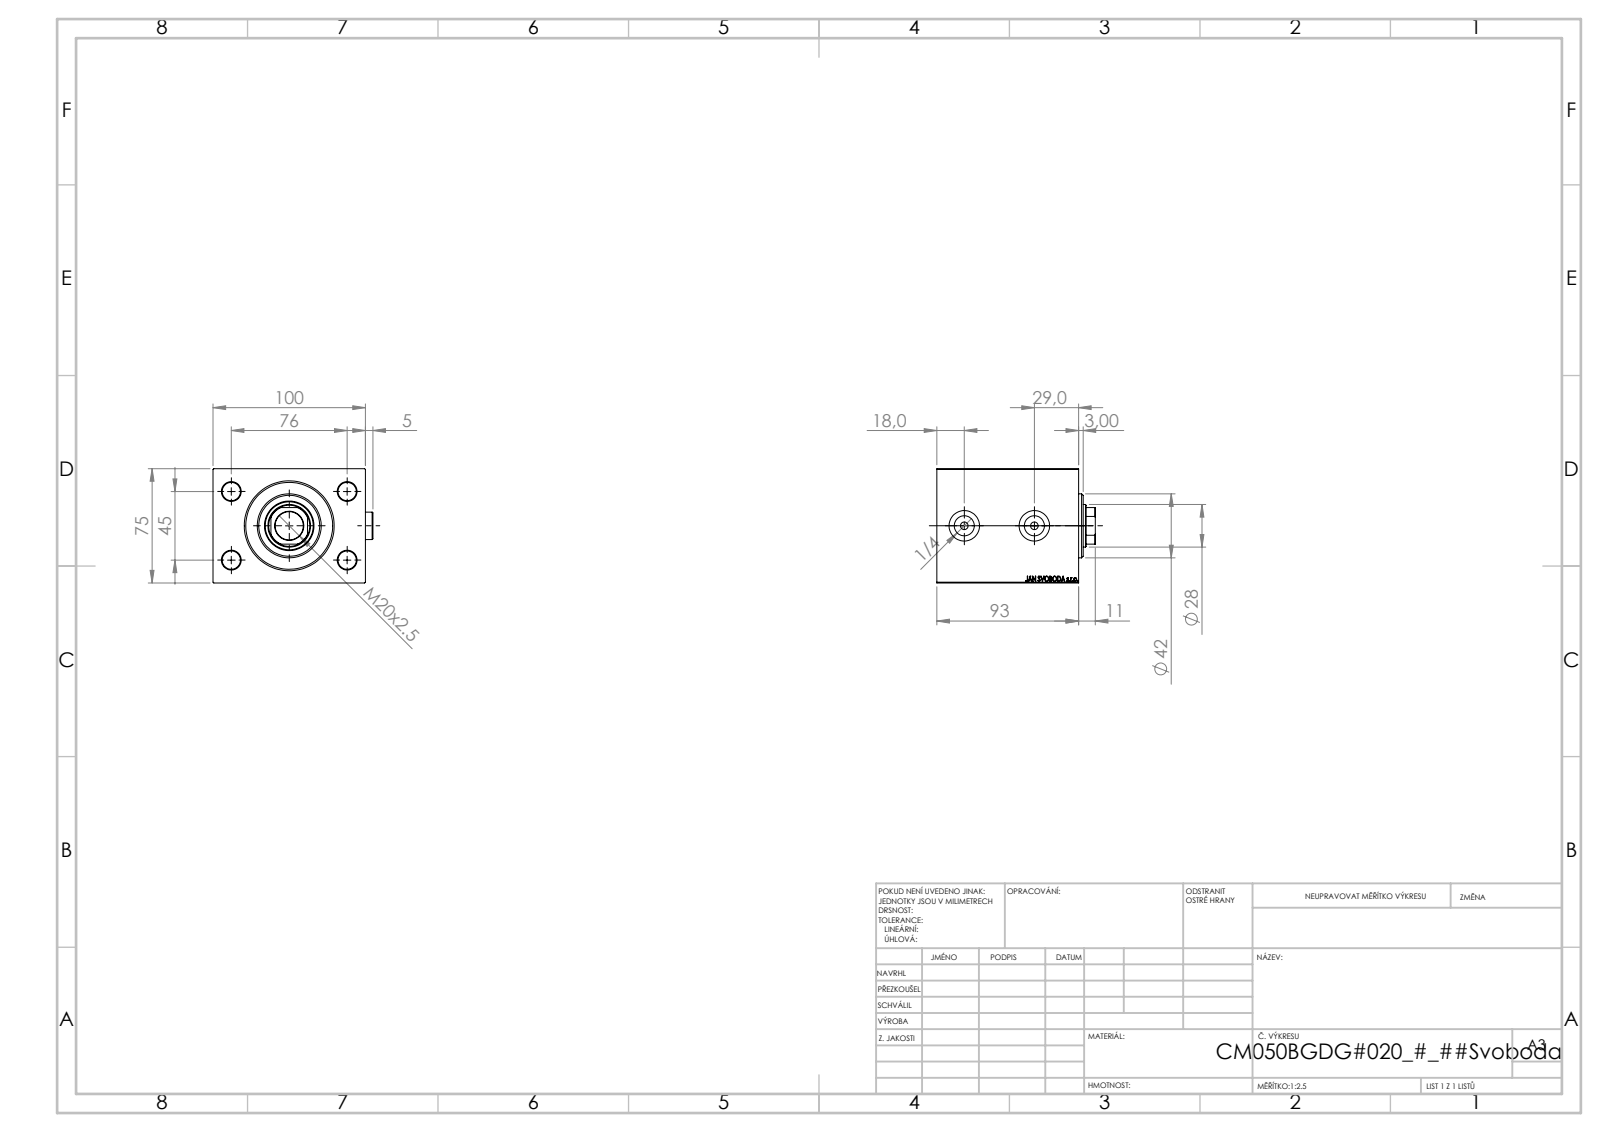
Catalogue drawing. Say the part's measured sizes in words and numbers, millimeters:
The part is named "V450CM_B_Body; Zatka_OIL_PORT; V450CM_VC_B; V450CM_B_VCP". Its 3-D file was written by "SolidWorks 2019 (CONFIG_CONTROL_DESIGN)". It is 5 solids with 936 faces: 436 planar, 70 cylindrical and 430 other. Overall it measures 104.9 by 104 by 75 millimeters. Its volume is 658 804 cubic millimeters and its surface area 89 193 square millimeters. Round holes: 4 of diameter 12, 2 of diameter 5, 2 of diameter 13.16, 2 of diameter 20, 1 of diameter 18.5, 1 of diameter 28, 1 of diameter 31.5, 1 of diameter 32.5, 1 of diameter 50, 1 of diameter 52, 1 of diameter 57. Round bosses or shafts: 2 of diameter 18, 1 of diameter 42. Partial cylindrical surfaces (rounded edges, fillets, slot ends): 1 of radius 13.5. The main face-to-face distances are 75, 100, 93, 42, 51, 21.6, 29.4, 71.4, 10, 31.6. The hole center spacings are 44.16, 45, 76, 88.32, 46.
